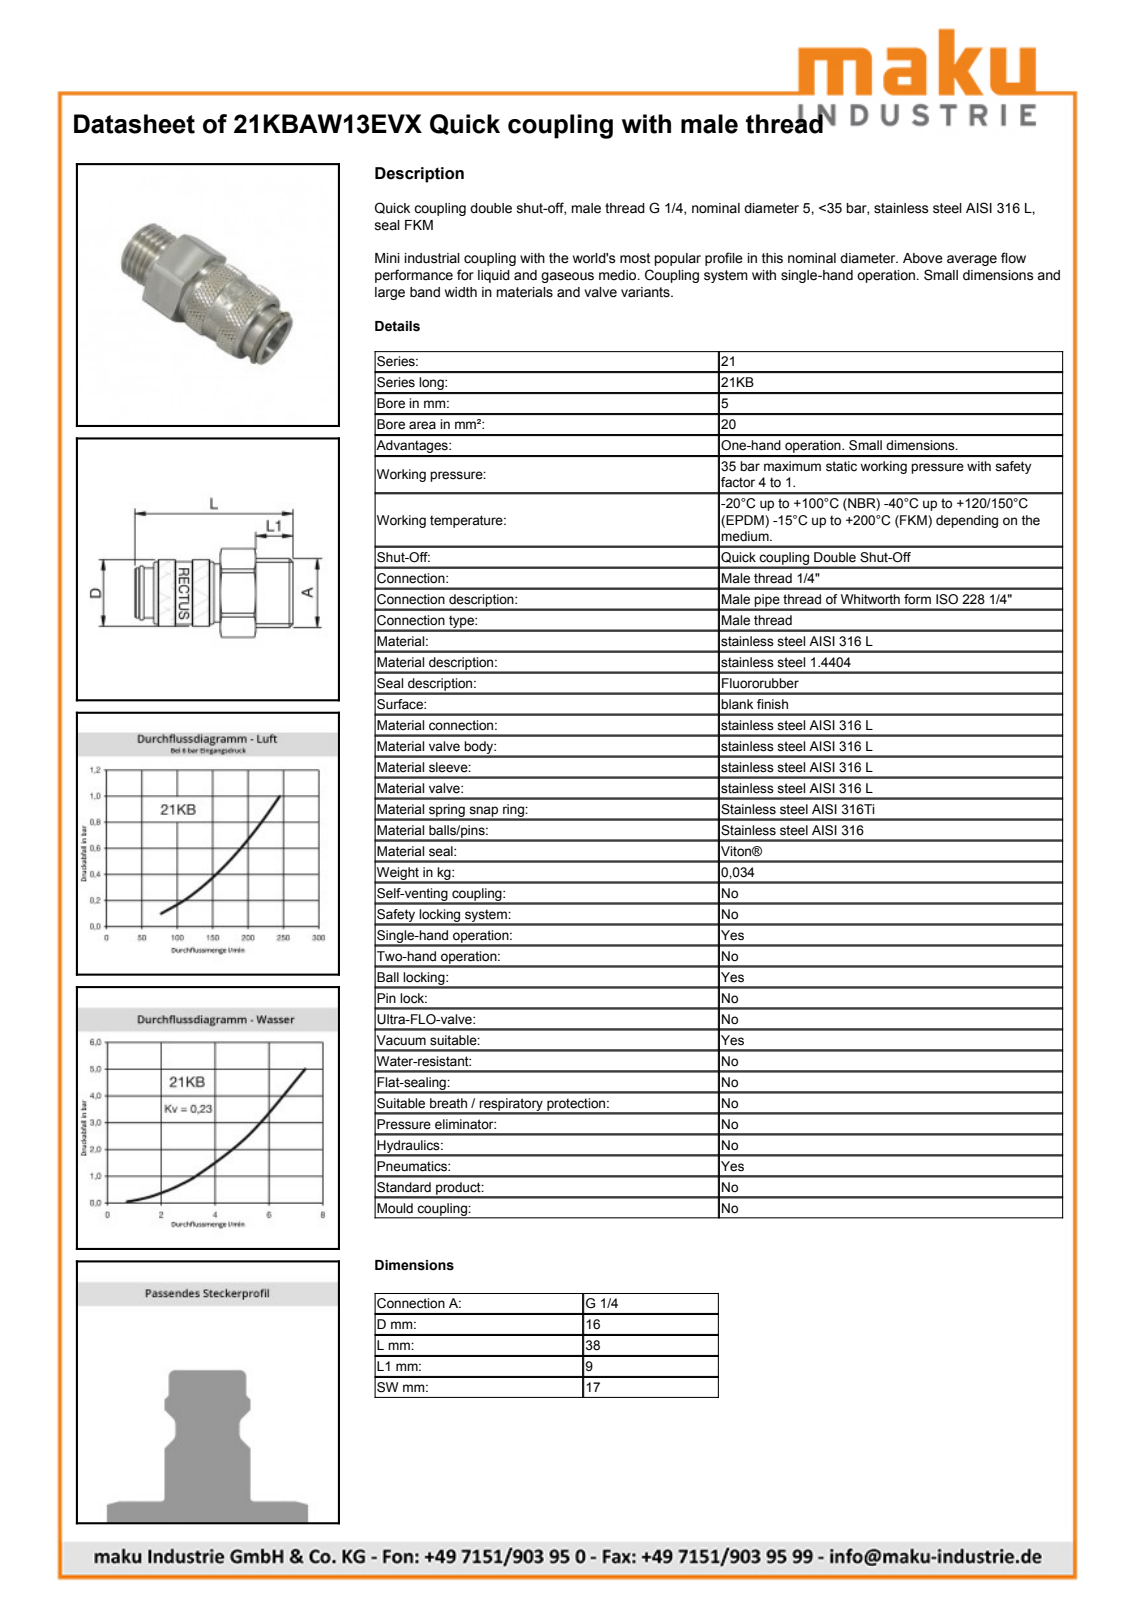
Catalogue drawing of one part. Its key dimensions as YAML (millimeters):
part_name: "D109000"
step_written_by: "Autodesk Inventor 2013 (AUTOMOTIVE_DESIGN)"
units: millimeters
bodies: {solids: 2, faces: 404, planar: 165, cylindrical: 65, other: 174}
overall_size: [38.15, 19.15, 17.45]
volume: 6503
surface_area: 3890
round_holes:
  - {diameter: 12.15, count: 1}
  - {diameter: 14, count: 1}
round_bosses_or_shafts:
  - {diameter: 16.15, count: 1}
  - {diameter: 15.1, count: 1}
  - {diameter: 13.8, count: 1}
  - {diameter: 13.16, count: 1}
  - {diameter: 12, count: 1}
  - {diameter: 11.4, count: 1}
  - {diameter: 11.15, count: 1}
partial_cylinders:
  - {radius: 5.54, count: 1}
  - {radius: 7.45, count: 1}
  - {radius: 9.57, count: 1}
face_to_face_distances: [17, 38.15, 9, 29.15, 20.6, 8.55, 17.55, 24.55, 4.6, 16]
